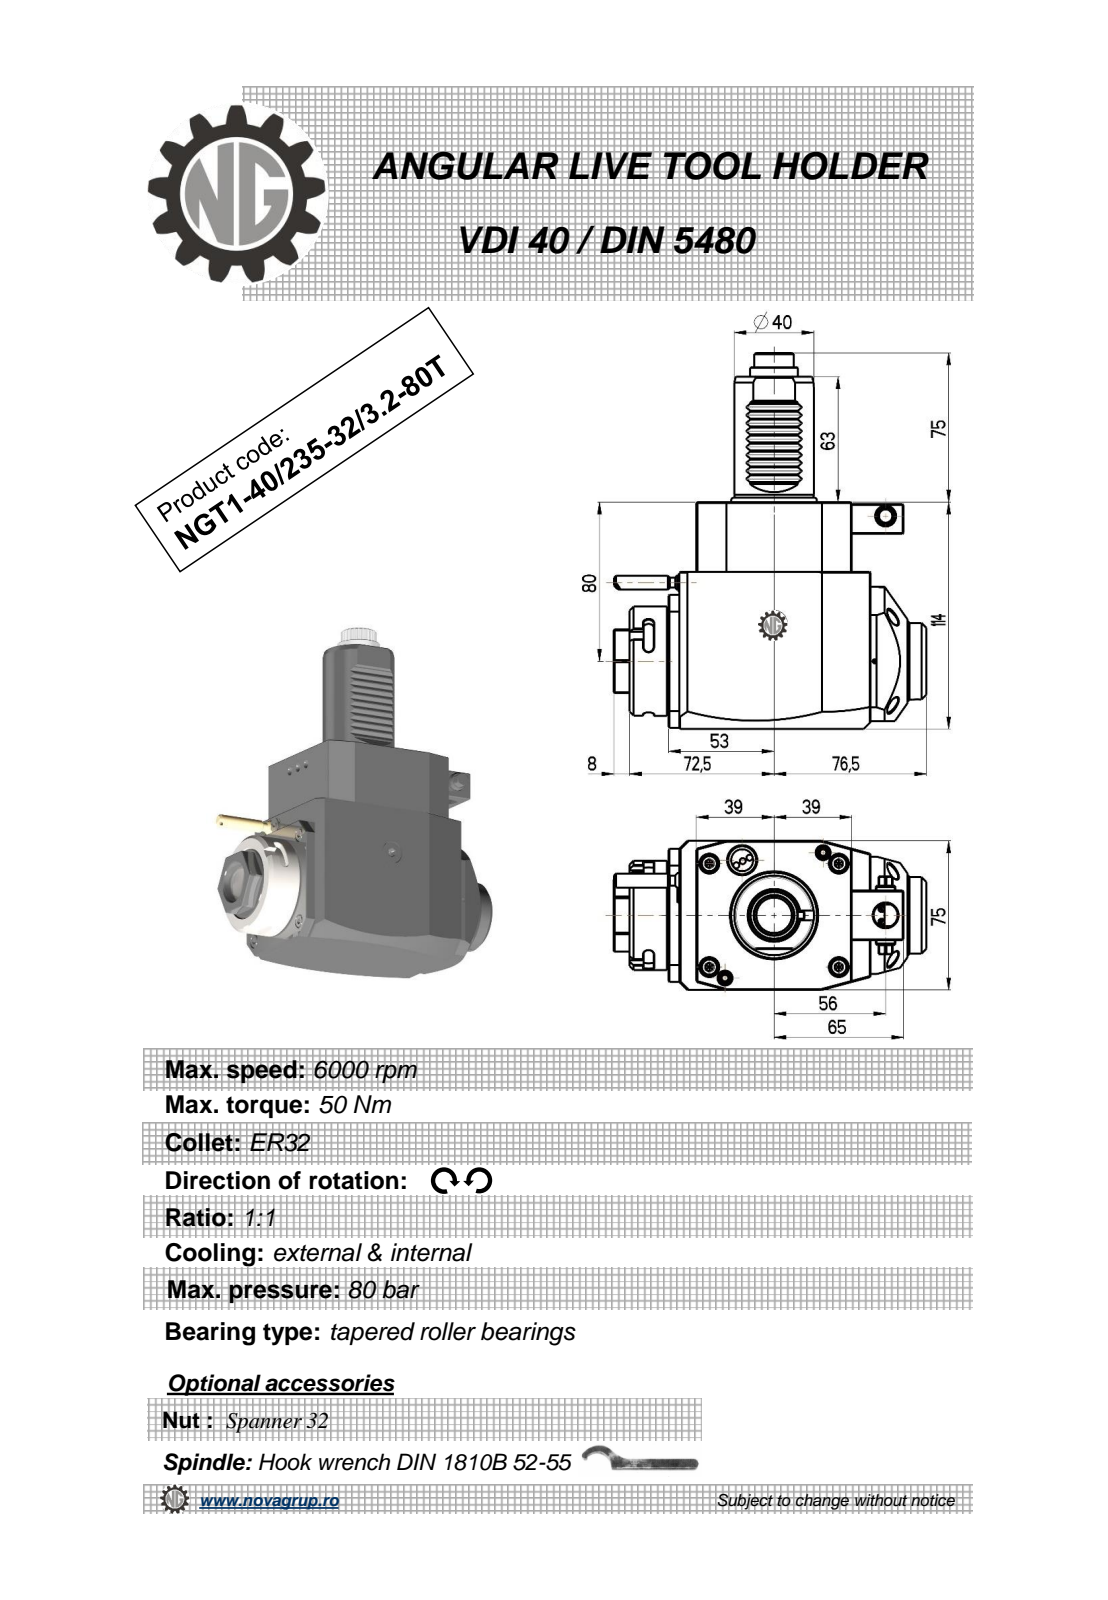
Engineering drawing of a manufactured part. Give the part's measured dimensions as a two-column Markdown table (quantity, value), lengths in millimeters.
| quantity | value |
| --- | --- |
| part name | NGT1_40_235_32_3_2_80T |
| STEP written by | PRO/ENGINEER BY PARAMETRIC TECHNOLOGY CORPORATION, 2010280 (CONFIG_CONTROL_DESIGN) |
| units | millimeters |
| bodies | 1 solid, 462 faces (192 planar, 174 cylindrical, 96 other) |
| overall size | 189 × 157 × 75 |
| volume | 976 578 mm³ |
| surface area | 72 910 mm² |
| round holes (diameter × count) | 2.5 × 1, 3 × 1, 9.5 × 1, 12 × 1, 23 × 1 |
| round bosses / shafts (diameter × count) | 8 × 2, 55 × 1, 48 × 1, 40 × 1, 38.5 × 1, 24 × 1, 10 × 1, 7 × 1 |
| partial cylindrical surfaces (radius × count) | 2.08 × 48, 0.3 × 10, 2.5 × 6, 180 × 2, 3.85 × 1, 4.25 × 1, 9.08 × 1, 9.92 × 1 |
| main face-to-face distances | 75, 114, 14, 92, 78, 79, 25, 19.5, 33.5, 111.5 |
| hole center spacings | 36.47, 43.2, 71.5 |
